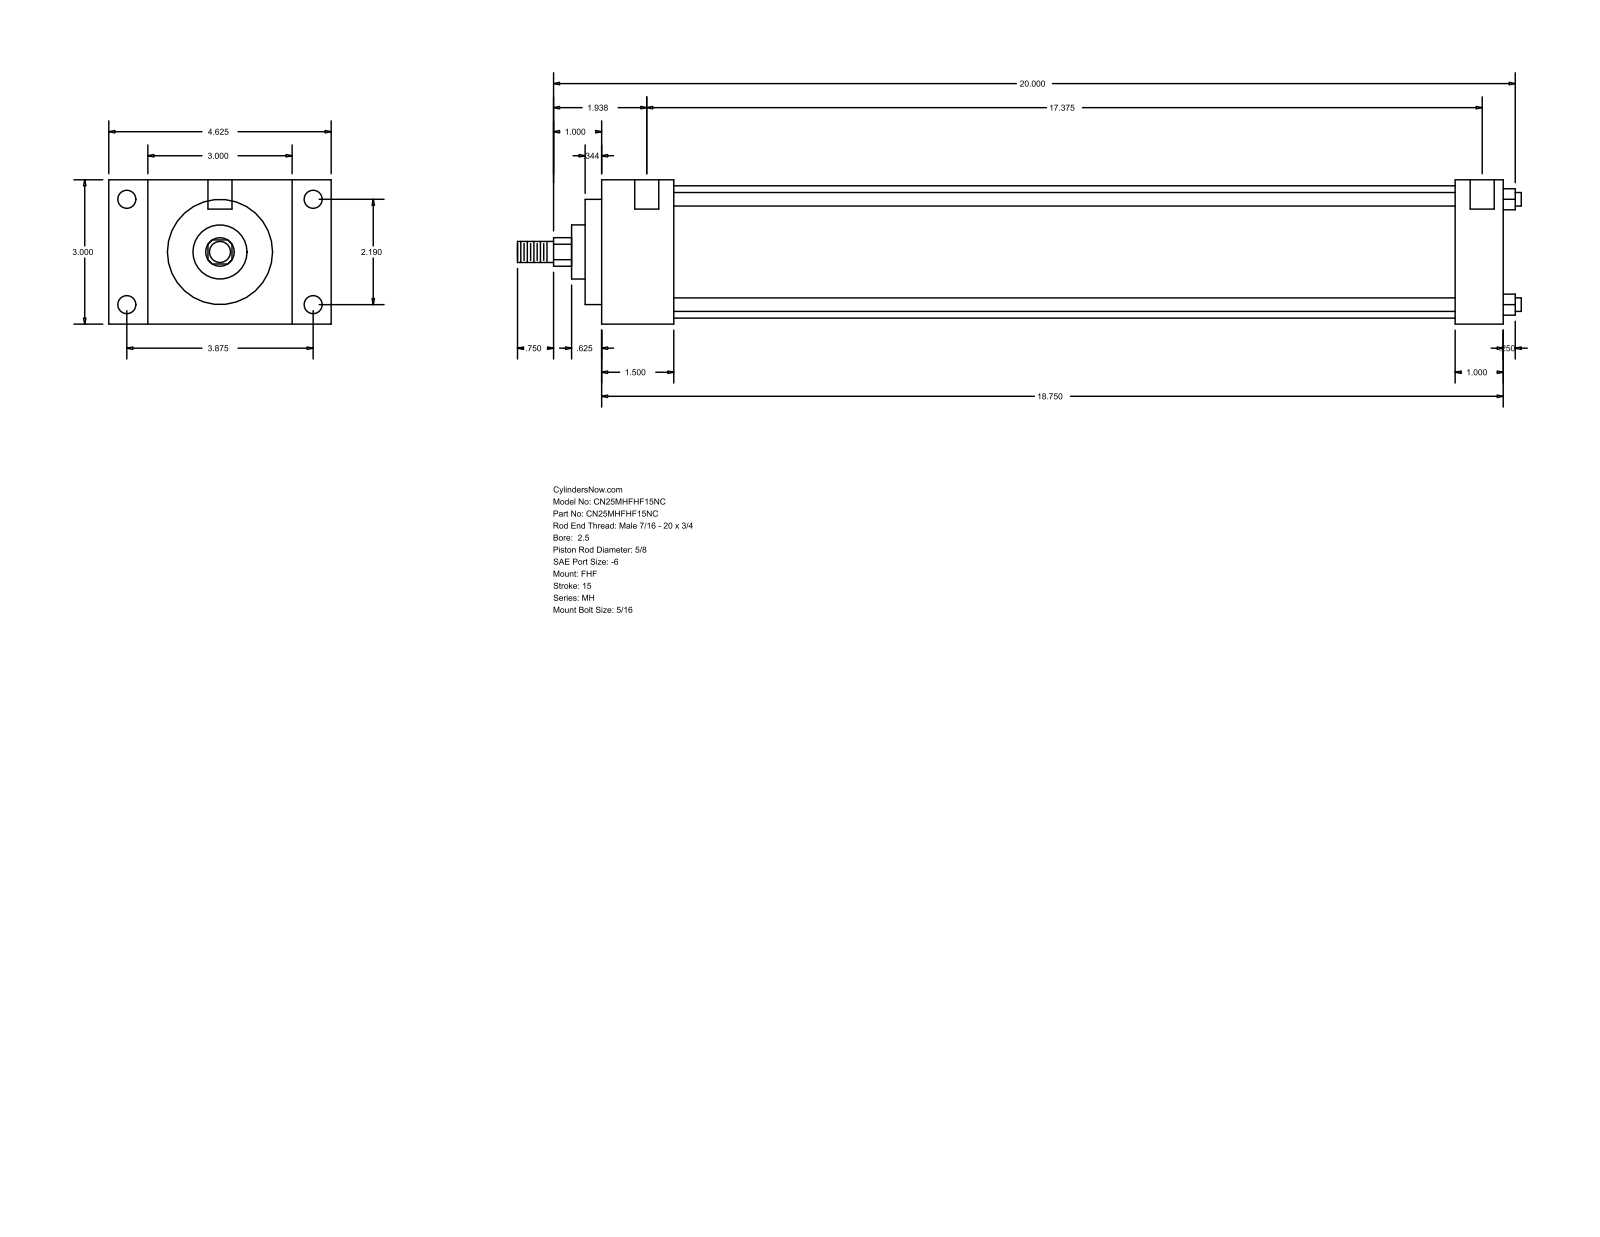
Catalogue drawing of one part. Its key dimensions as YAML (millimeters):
part_name: "MH_FHF__0250_0.625"
step_written_by: "GSSL Pune (CONFIG_CONTROL_DESIGN)"
units: millimeters
bodies: {solids: 0, faces: 90, planar: 61, cylindrical: 29, other: 0}
overall_size: [530.23, 117.47, 76.2]
round_holes:
  - {diameter: 5.56, count: 4}
  - {diameter: 9.53, count: 4}
  - {diameter: 12.7, count: 2}
round_bosses_or_shafts:
  - {diameter: 7.14, count: 4}
  - {diameter: 69.85, count: 1}
  - {diameter: 55.55, count: 1}
  - {diameter: 28.57, count: 1}
  - {diameter: 15.88, count: 1}
  - {diameter: 11.11, count: 1}
partial_cylinders:
  - {radius: 7.54, count: 1}
face_to_face_distances: [76.2, 476.25, 38.1, 438.15, 20.64, 96.84, 117.48, 25.4, 450.85, 412.75]
hole_center_spacings: [55.62, 98.42, 113.05, 449.26, 3.17, 4.76, 441.33, 444.5]
